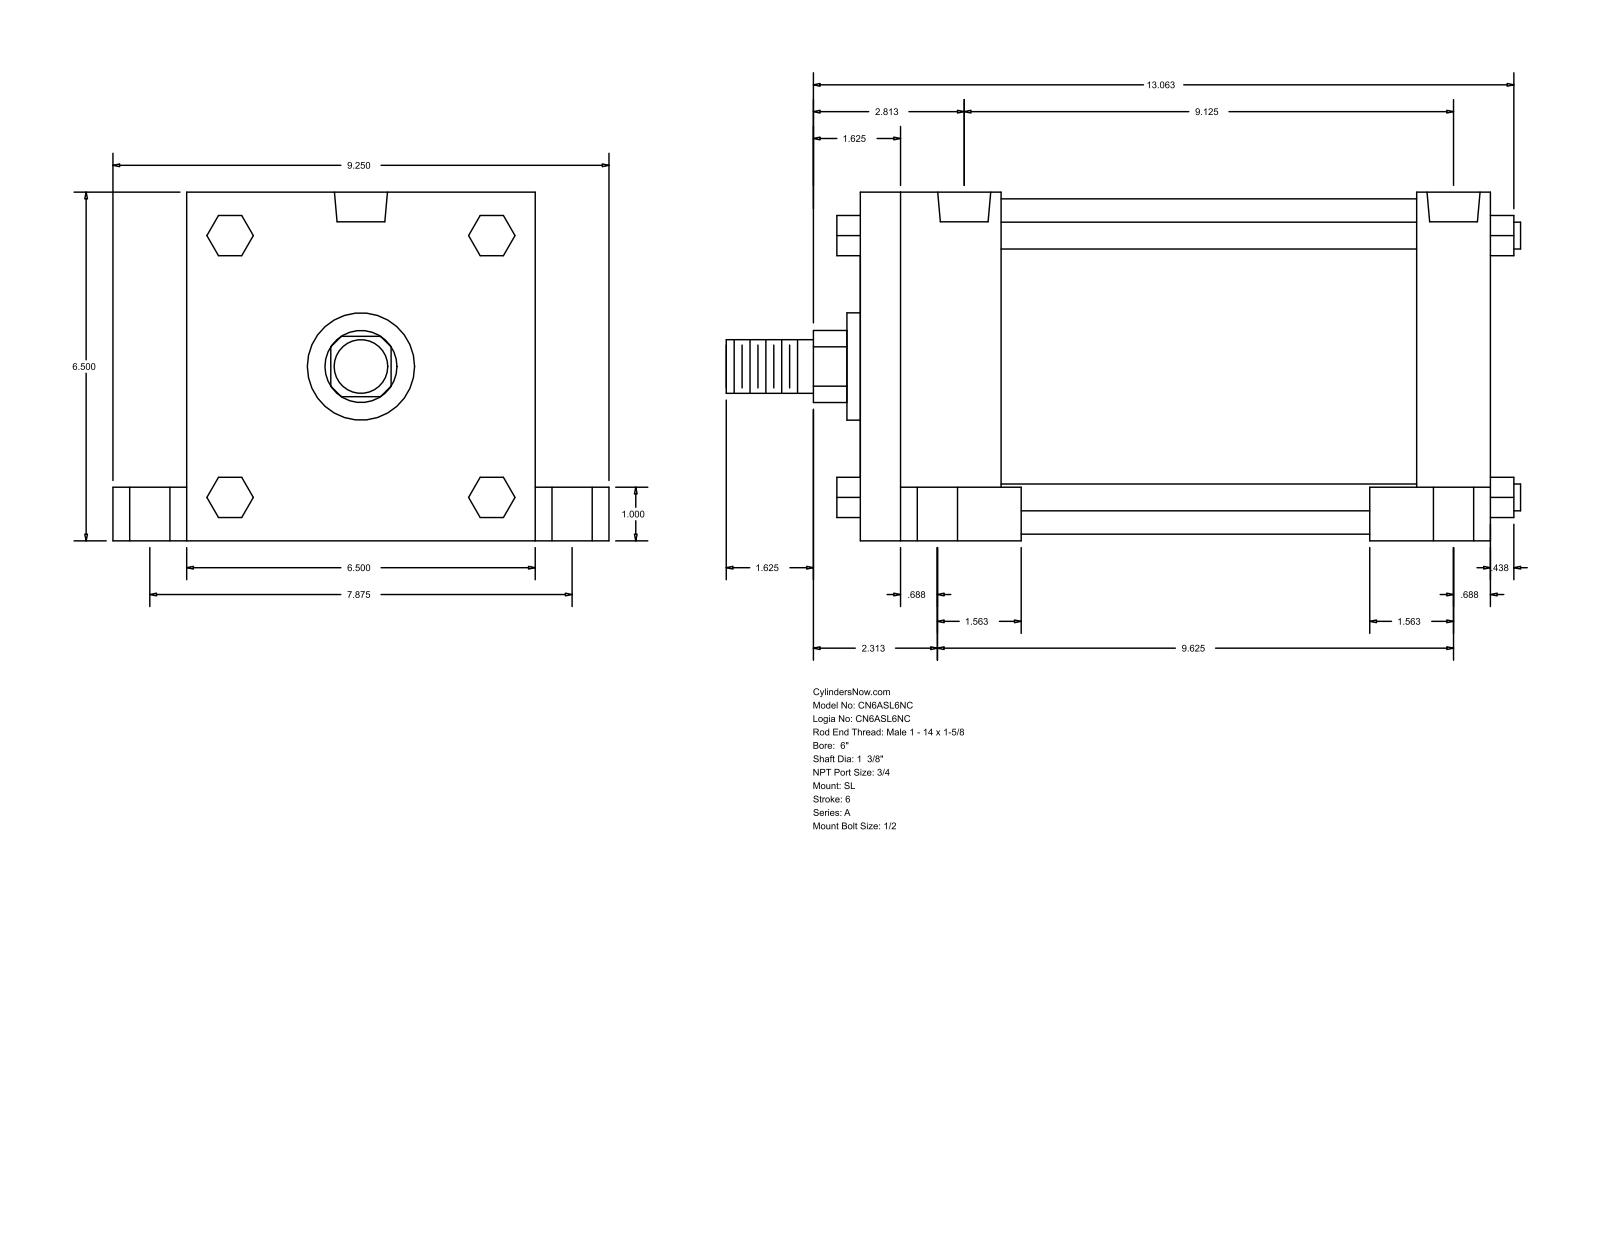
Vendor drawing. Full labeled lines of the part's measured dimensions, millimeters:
Part name (STEP PRODUCT): A_SL__0600_1.375
STEP written by: GSSL Pune (CONFIG_CONTROL_DESIGN)
Units: millimetres
Bodies: 0 solids, 150 faces (114 planar, 36 cylindrical, 0 other)
Overall size (bounding box): 376.24 × 234.95 × 165.1
Round holes (diameter × count): ⌀15.08 ×4, ⌀19.05 ×4, ⌀25.4 ×4, ⌀25.12 ×2
Round bosses / shafts (diameter × count): ⌀12.7 ×4, ⌀158.75 ×1, ⌀50.8 ×1, ⌀34.92 ×1, ⌀25.4 ×1
Partial cylindrical surfaces — rounded edges, fillets, slot ends (radius × count): R17.06 ×1
Main face-to-face distances: 165.1, 298.45, 263.52, 66.67, 231.78, 196.85, 34.93, 25.4, 139.7, 34.92
Hole centre spacings: 5.56, 100.01, 100.16, 100.81, 101.66, 200.02, 220.65, 226.21
